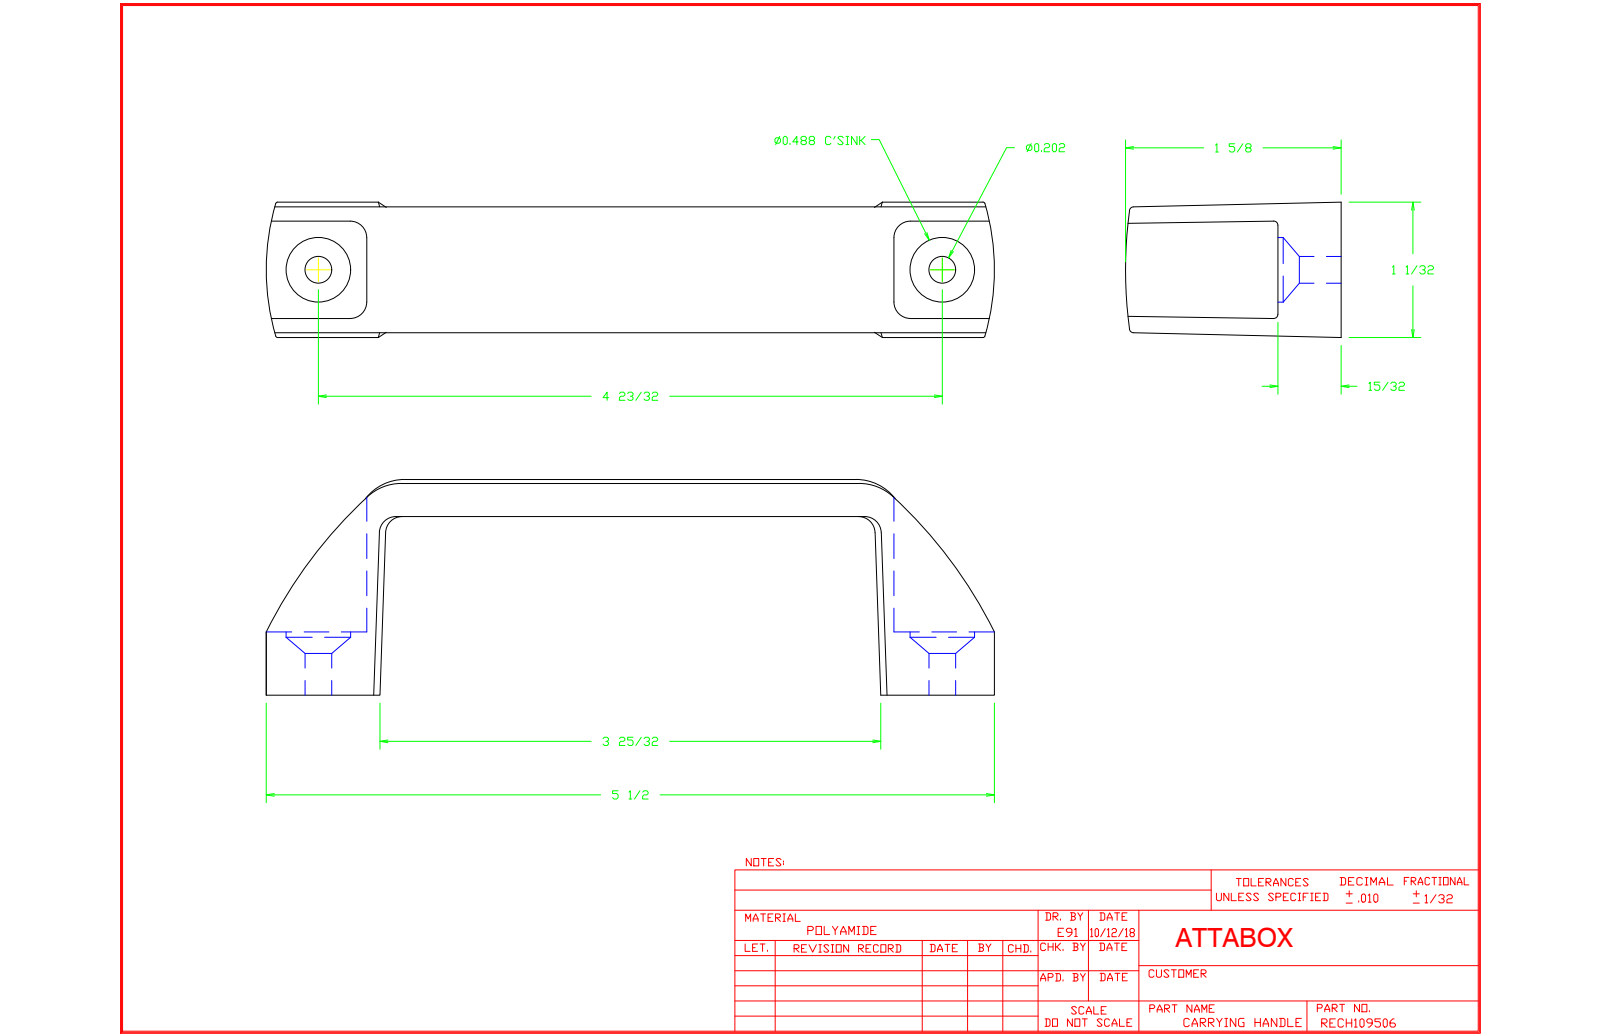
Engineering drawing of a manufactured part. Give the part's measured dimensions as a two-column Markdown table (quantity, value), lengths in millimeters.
| quantity | value |
| --- | --- |
| part name | RECH109506 |
| STEP written by | SolidWorks 2017 (AUTOMOTIVE_DESIGN) |
| units | millimeters |
| bodies | 1 solid, 71 faces (20 planar, 22 cylindrical, 29 other) |
| overall size | 142 × 39.9 × 26 |
| volume | 37 220 mm³ |
| surface area | 15 280 mm² |
| round holes (diameter × count) | 5.3 × 2, 13.3 × 2 |
| partial cylindrical surfaces (radius × count) | 1.3 × 10, 2.5 × 4, 3.2 × 2, 61.9 × 2 |
| main face-to-face distances | 8.1, 31.8, 39.9, 12, 19.8, 27.9, 37.4, 25.4, 5.6, 2.5 |
| hole center spacings | 121.9 |
